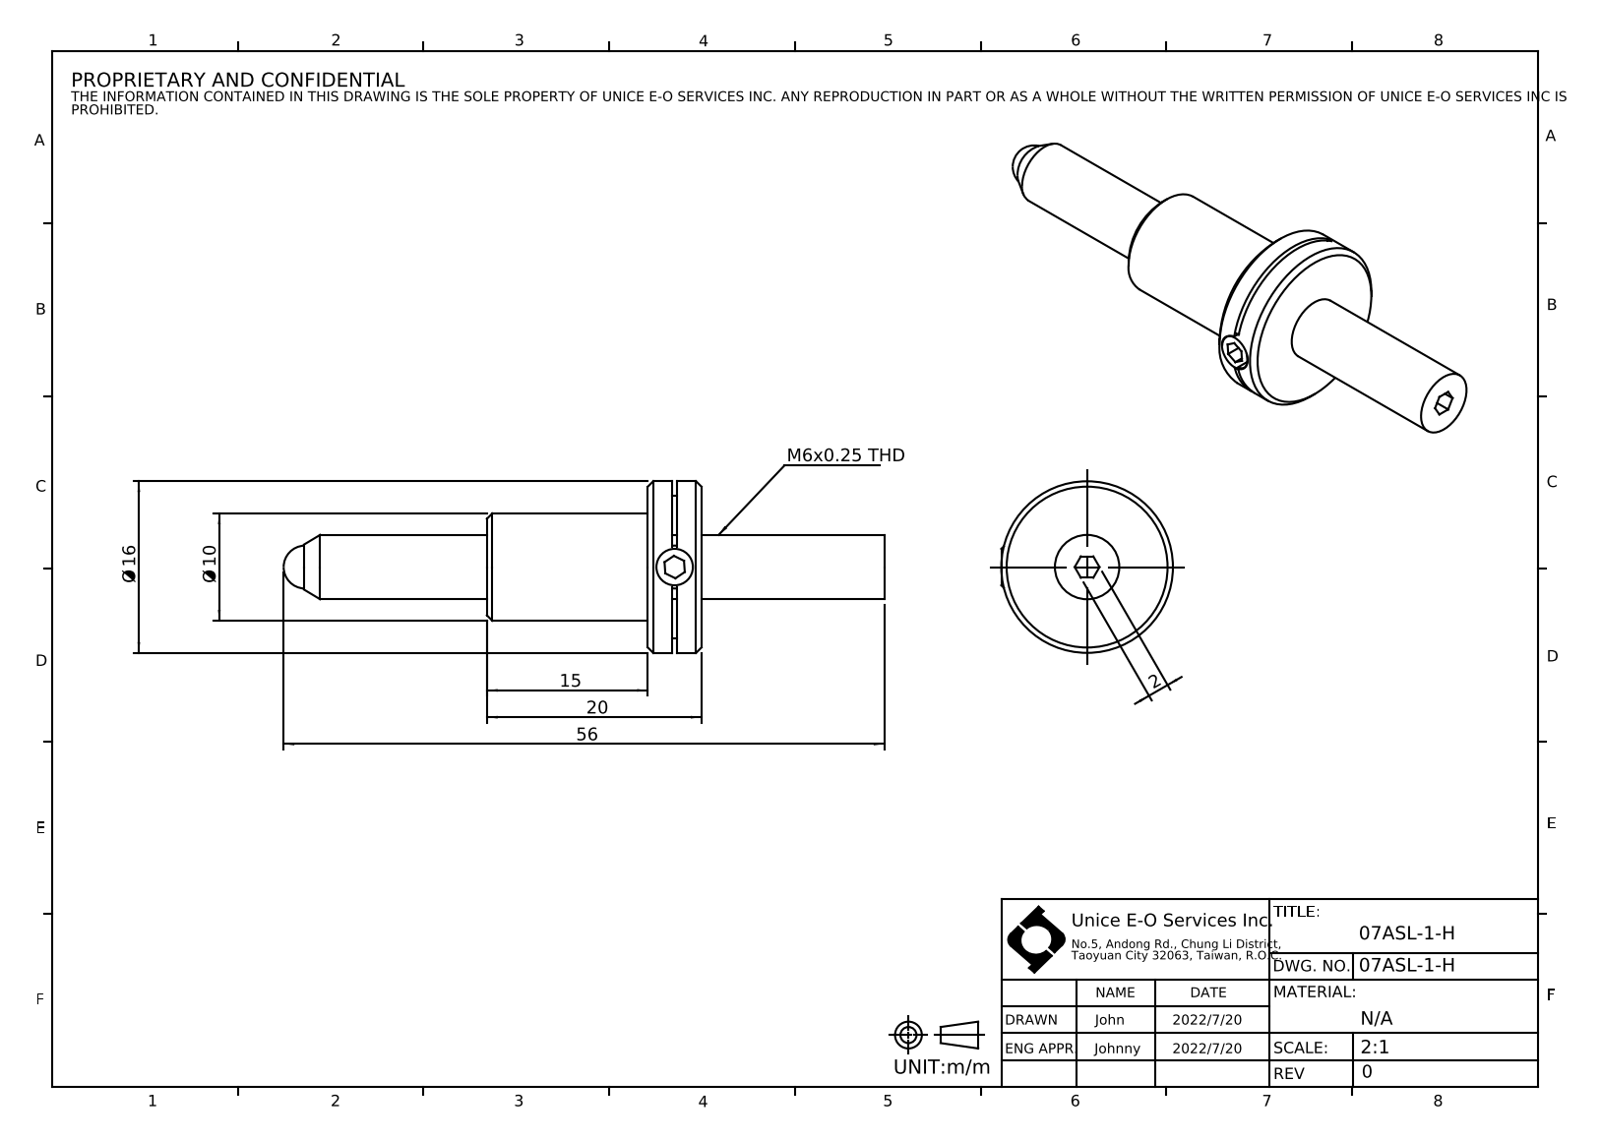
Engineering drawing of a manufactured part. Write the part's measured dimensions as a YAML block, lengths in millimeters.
part_name: "07ASL-1-H"
step_written_by: "SolidWorks 2021 (CONFIG_CONTROL_DESIGN)"
units: millimeters
bodies: {solids: 4, faces: 64, planar: 24, cylindrical: 17, other: 23}
overall_size: [56, 16, 16]
volume: 3230
surface_area: 2875
round_holes:
  - {diameter: 3.3, count: 1}
  - {diameter: 4, count: 1}
  - {diameter: 5, count: 1}
round_bosses_or_shafts:
  - {diameter: 16, count: 1}
  - {diameter: 10, count: 1}
  - {diameter: 6, count: 1}
  - {diameter: 4, count: 1}
face_to_face_distances: [2.25, 2.75, 0.5, 5, 15, 17.25, 17.75, 20, 17.05, 37.05]
